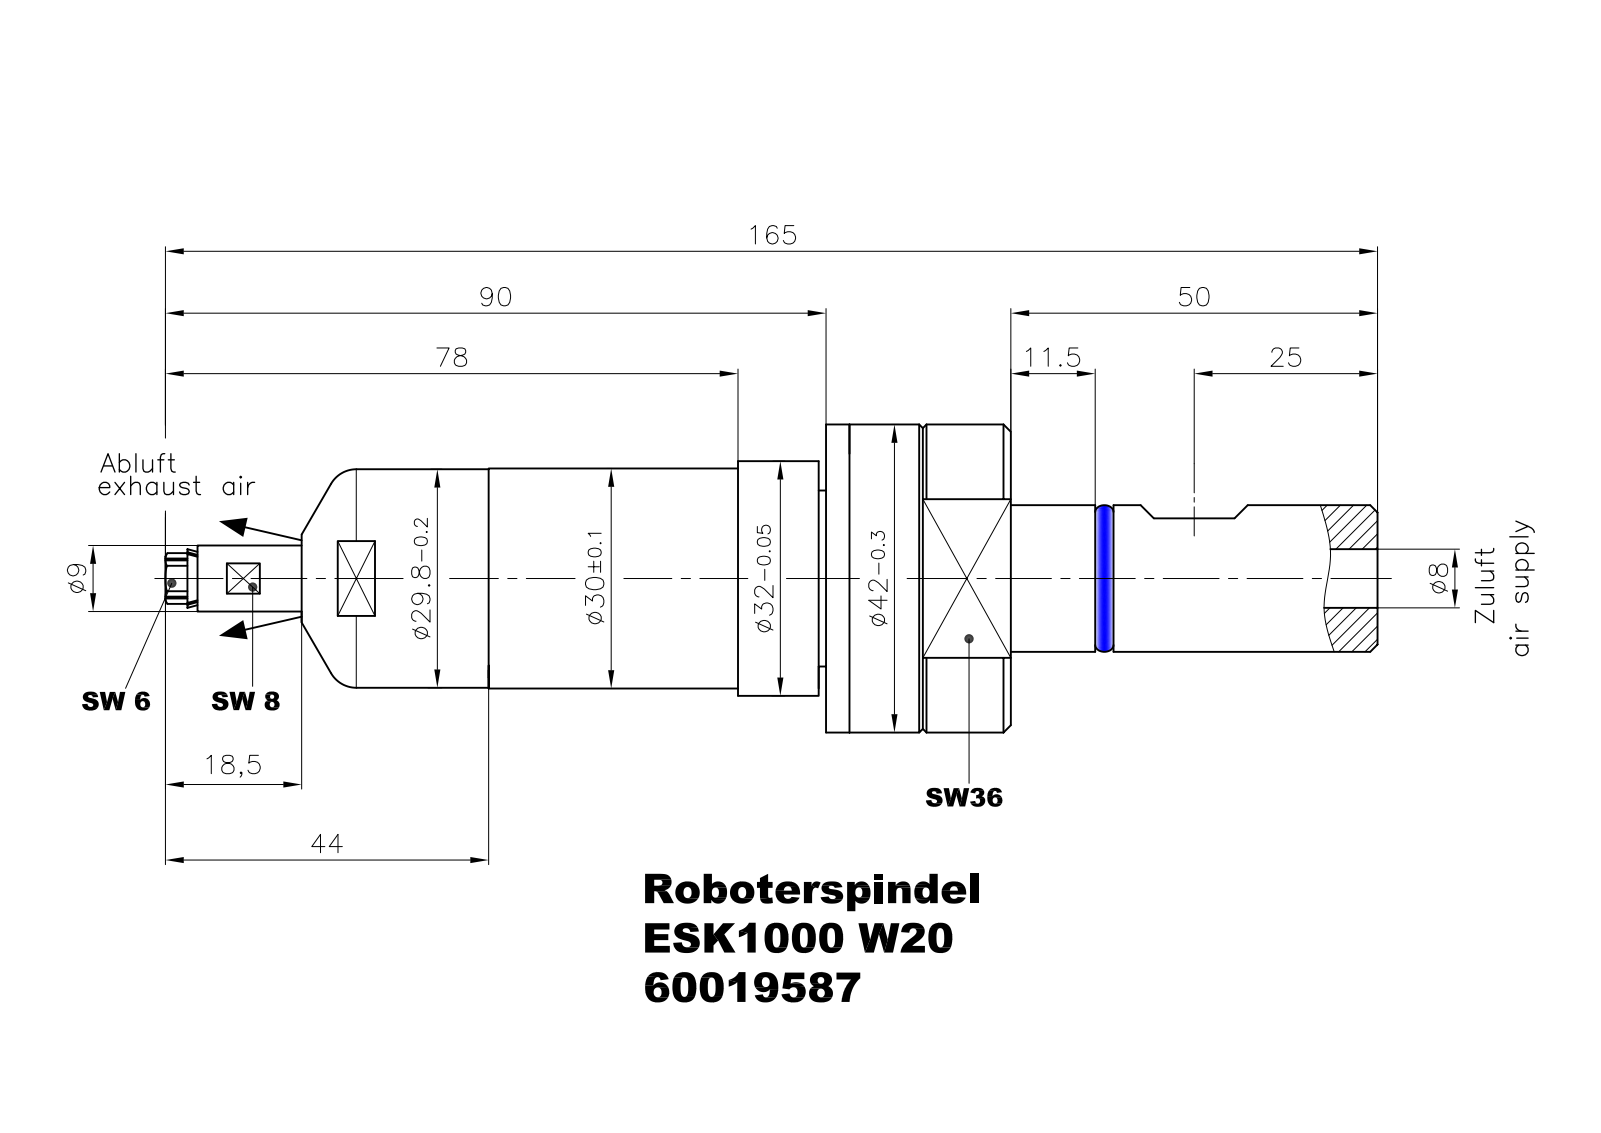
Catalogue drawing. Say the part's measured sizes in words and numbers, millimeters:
The part is named "ESK 1000 W20_60019587". Its 3-D file was written by "Autodesk Inventor 2012 (AUTOMOTIVE_DESIGN)". It is 1 solid with 116 faces: 60 planar, 31 cylindrical and 25 other. Overall it measures 164.88 by 42 by 42 millimeters. Its volume is 96 094 cubic millimeters and its surface area 19 908 square millimeters. Round holes: 2 of diameter 2.2, 1 of diameter 3, 1 of diameter 3.1, 1 of diameter 4.46, 1 of diameter 5, 1 of diameter 8, 1 of diameter 11, 1 of diameter 12, 1 of diameter 23.92. Round bosses or shafts: 1 of diameter 42, 1 of diameter 32, 1 of diameter 30, 1 of diameter 29.8, 1 of diameter 23.79, 1 of diameter 20, 1 of diameter 16.25, 1 of diameter 9. Partial cylindrical surfaces (rounded edges, fillets, slot ends): 3 of radius 5. The main face-to-face distances are 25.2, 36, 1.05, 26.25, 66.13, 67.18, 92.38, 142.38, 76.25, 75.2. The hole center spacings are 9.6, 19.2.
